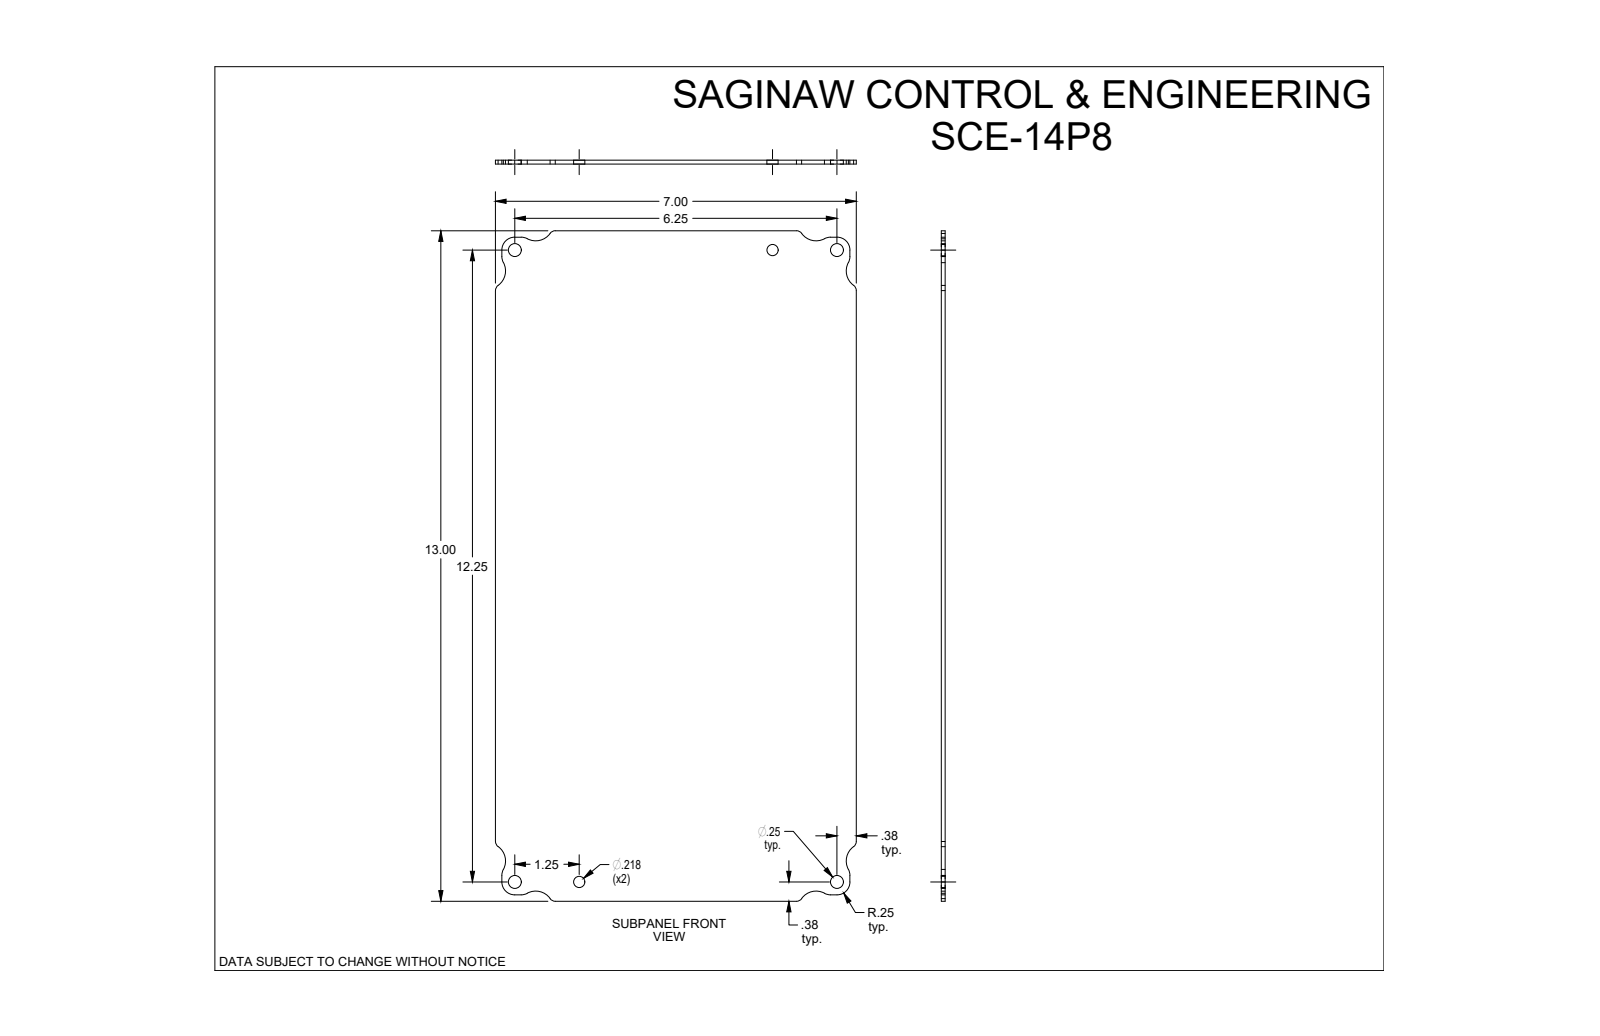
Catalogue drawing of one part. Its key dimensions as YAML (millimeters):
part_name: "SCE-14P8"
step_written_by: "SolidWorks 2019 (CONFIG_CONTROL_DESIGN)"
units: millimeters
bodies: {solids: 1, faces: 48, planar: 14, cylindrical: 34, other: 0}
overall_size: [330.2, 177.8, 1.9]
volume: 110000
surface_area: 117600
round_holes:
  - {diameter: 6.4, count: 4}
  - {diameter: 5.5, count: 2}
partial_cylinders:
  - {radius: 6.4, count: 12}
  - {radius: 3.2, count: 8}
  - {radius: 8.7, count: 8}
face_to_face_distances: [1.9, 177.8, 330.2, 3.1, 174.7, 3.2, 327, 171.5, 323.9]
hole_center_spacings: [31.8, 127, 158.8, 311.2, 312.8, 336.1, 349.3, 325.4]
